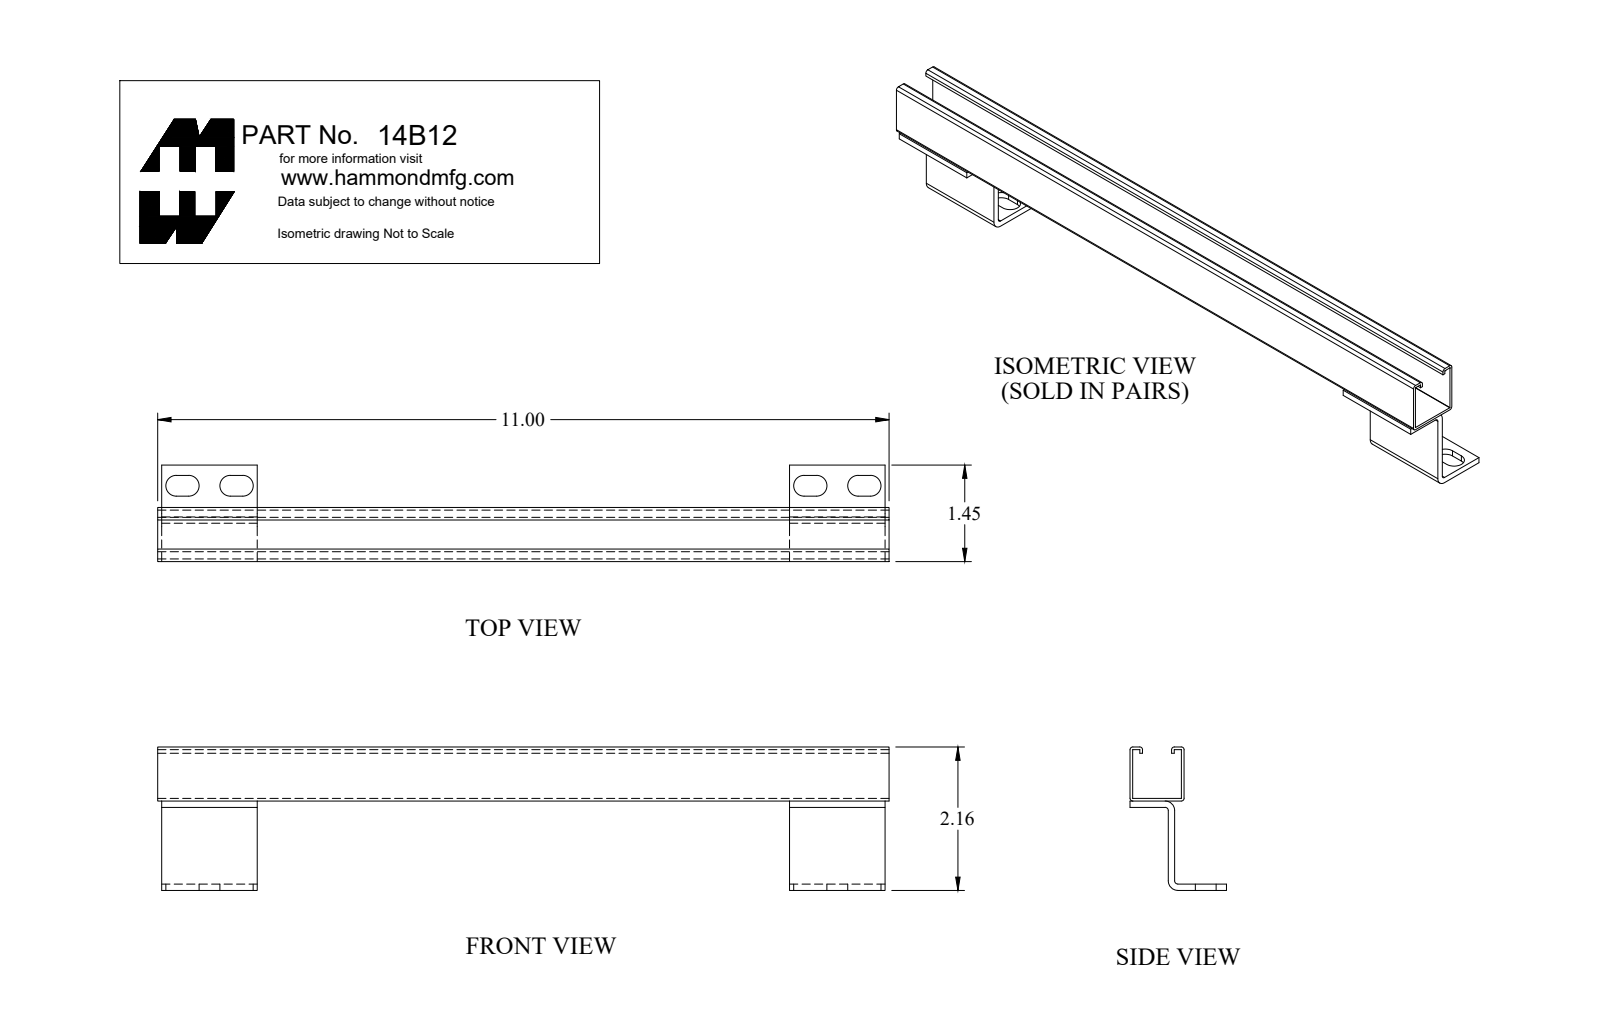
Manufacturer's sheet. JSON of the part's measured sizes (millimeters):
{"part_name": "14B12", "step_written_by": "SolidWorks 2018 (AUTOMOTIVE_DESIGN)", "units": "millimeters", "bodies": {"solids": 3, "faces": 74, "planar": 46, "cylindrical": 28, "other": 0}, "overall_size": [279.4, 54.8, 36.9], "volume_mm3": 30370, "surface_area_mm2": 49420, "partial_cylinders_radius": [[4, 8], [1.1, 6], [1.2, 2], [3.6, 2]], "face_to_face_distances": [1, 19.6, 20.7, 18.6, 2.4, 19.6, 31.7, 3.6, 6, 2.6]}
